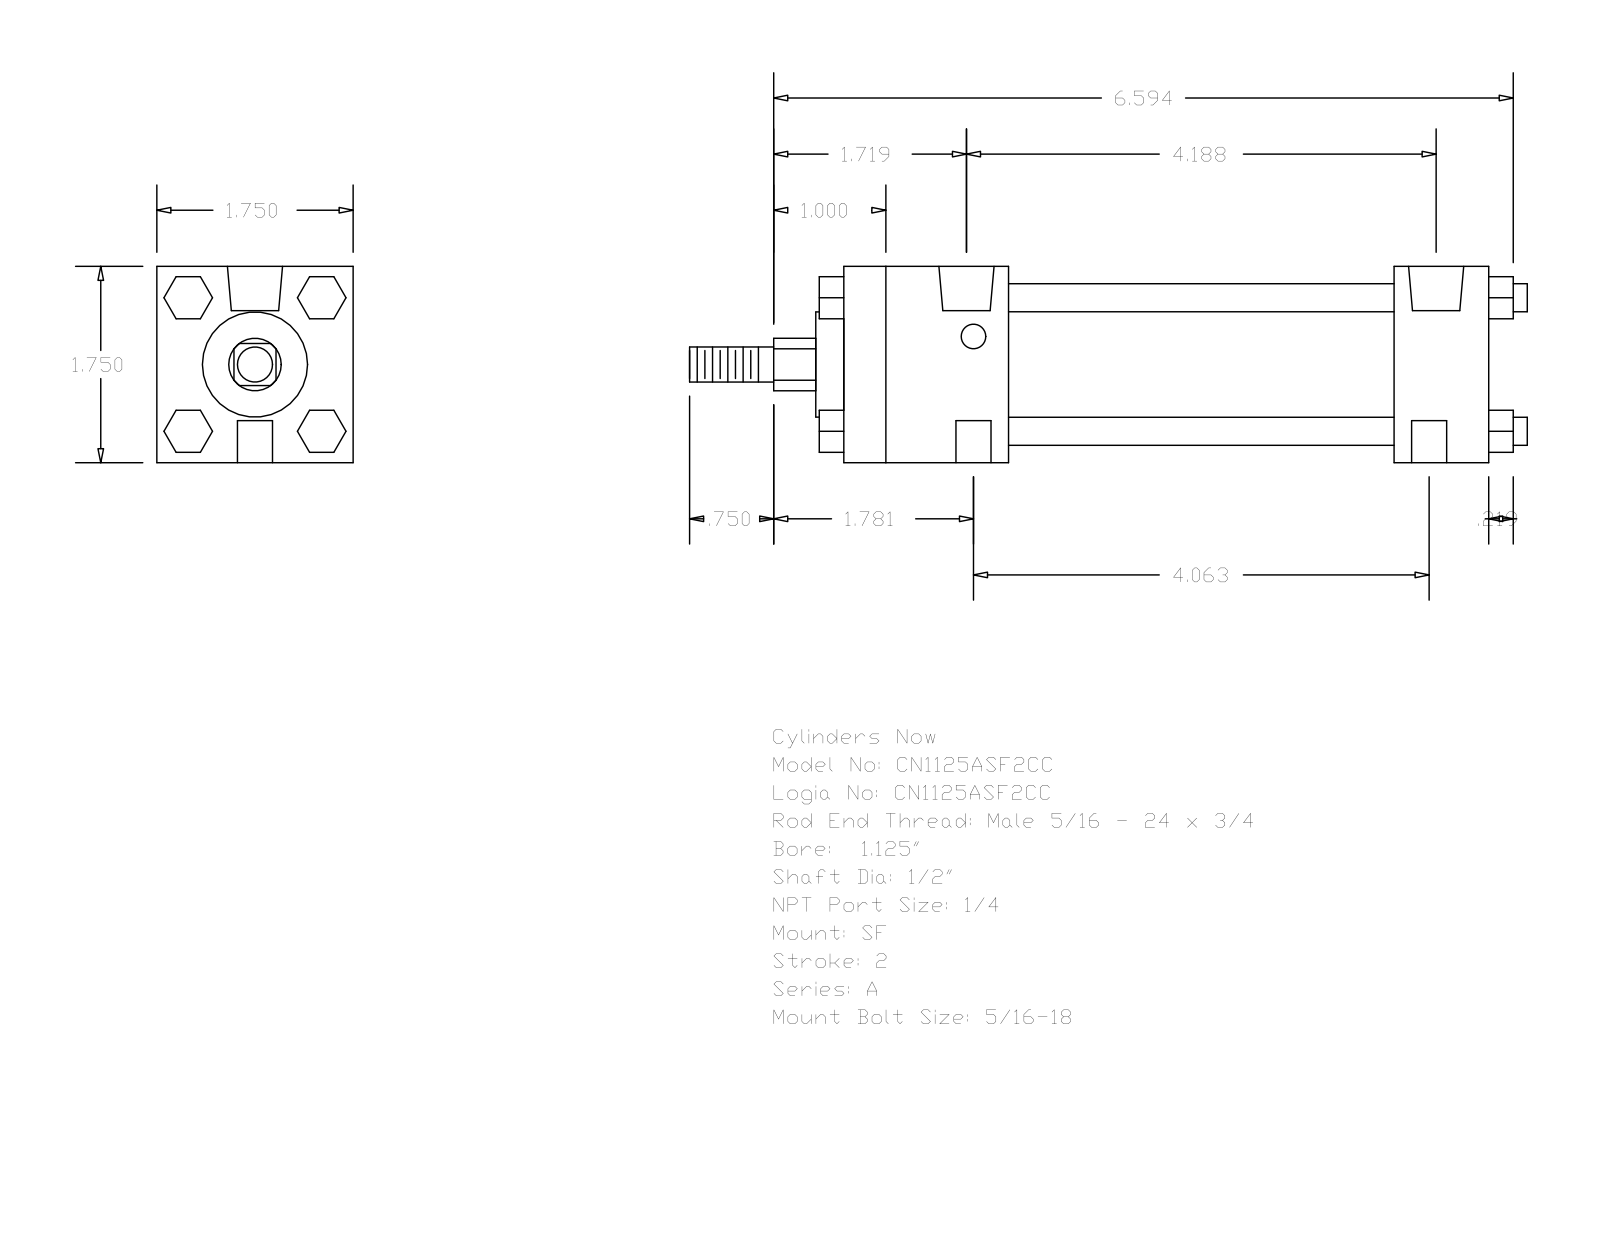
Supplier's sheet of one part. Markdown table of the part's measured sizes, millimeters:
| quantity | value |
| --- | --- |
| part name | A_SF__0112_0.5 |
| STEP written by | GSSL Pune (CONFIG_CONTROL_DESIGN) |
| units | millimeters |
| bodies | 0 solids, 120 faces (92 planar, 28 cylindrical, 0 other) |
| overall size | 189.71 × 44.45 × 44.45 |
| round holes (diameter × count) | 5.56 × 2, 7.94 × 2, 12.49 × 2 |
| round bosses / shafts (diameter × count) | 6.35 × 4, 31.88 × 1, 23.81 × 1, 12.7 × 1, 7.94 × 1 |
| partial cylindrical surfaces (radius × count) | 5.94 × 1 |
| main face-to-face distances | 44.46, 146.05, 124.61, 21.44, 37.3, 87.31, 108.75, 9.53, 5.59, 26.99 |
| hole center spacings | 103.19, 1.58, 1.59, 104.77, 104.78, 106.36 |
